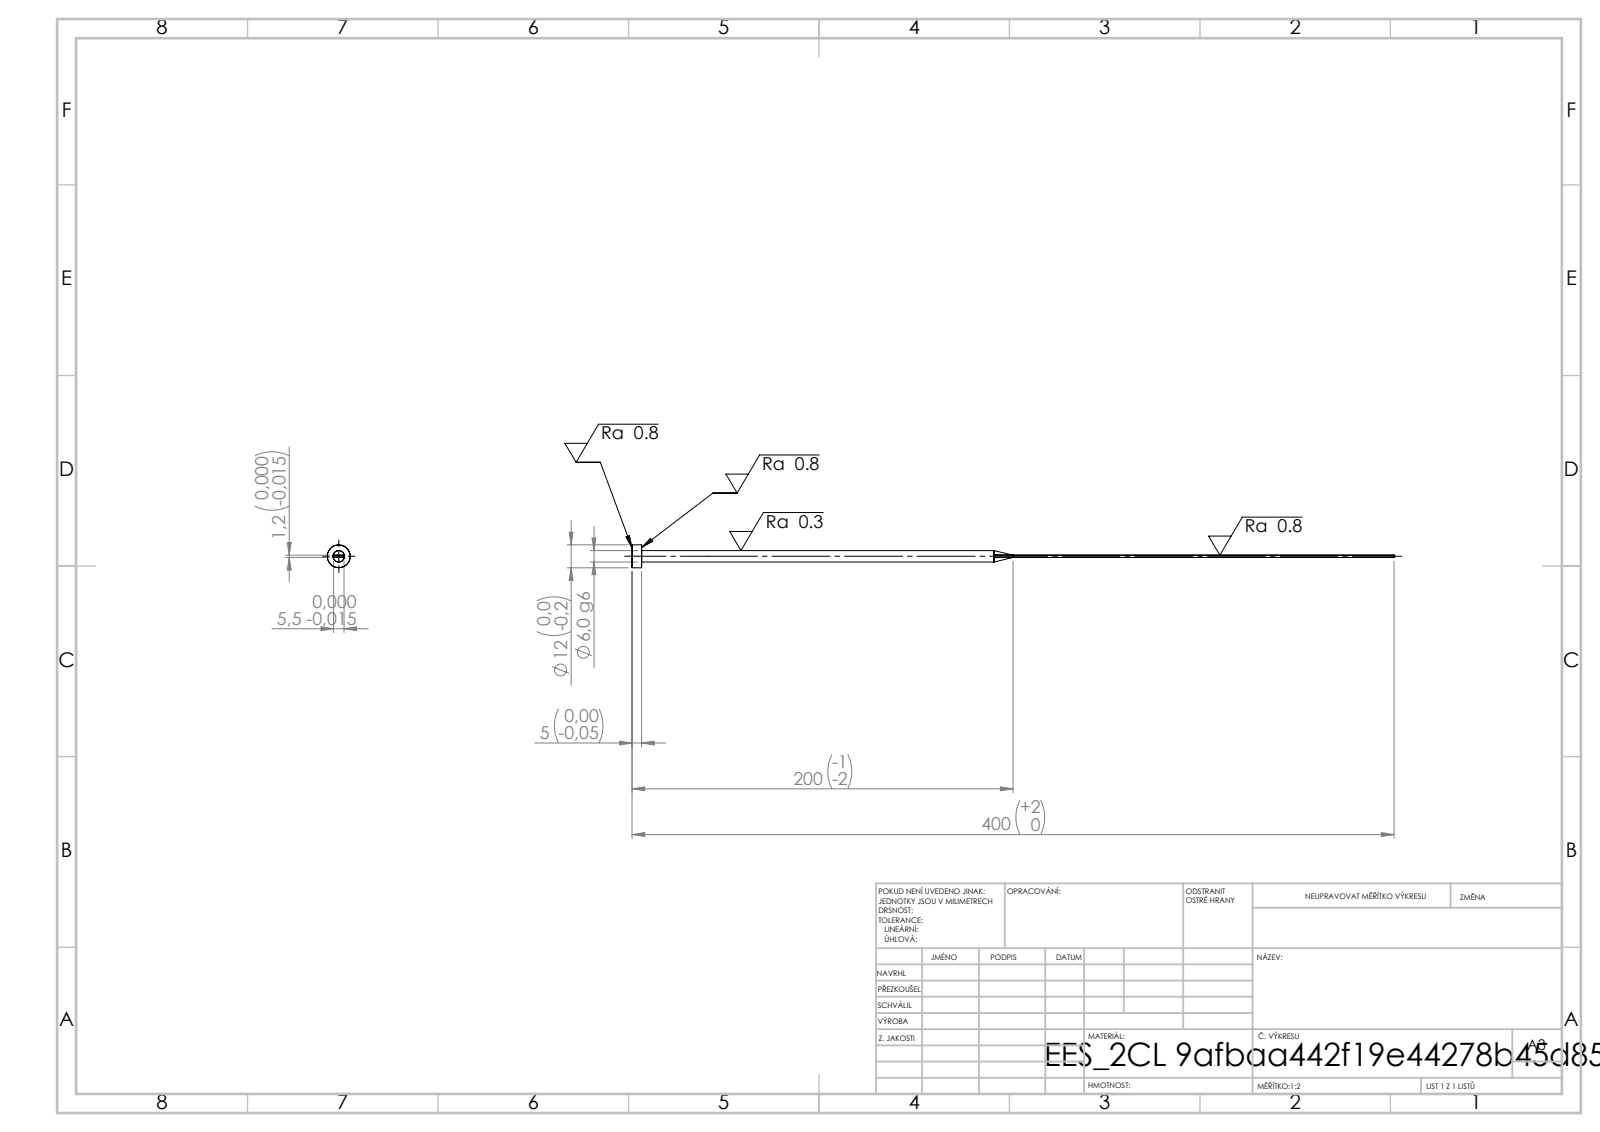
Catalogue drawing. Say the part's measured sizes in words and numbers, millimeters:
Its 3-D file was written by "SolidWorks 2019 (CONFIG_CONTROL_DESIGN)". It is 1 solid with 15 faces: 7 planar, 4 cylindrical and 4 other. Overall it measures 400 by 12 by 12 millimeters. Its volume is 7 282 cubic millimeters and its surface area 6 716 square millimeters. Round bosses or shafts: 1 of diameter 12, 1 of diameter 6. The main face-to-face distances are 1.2, 5.5, 5, 400, 395.
